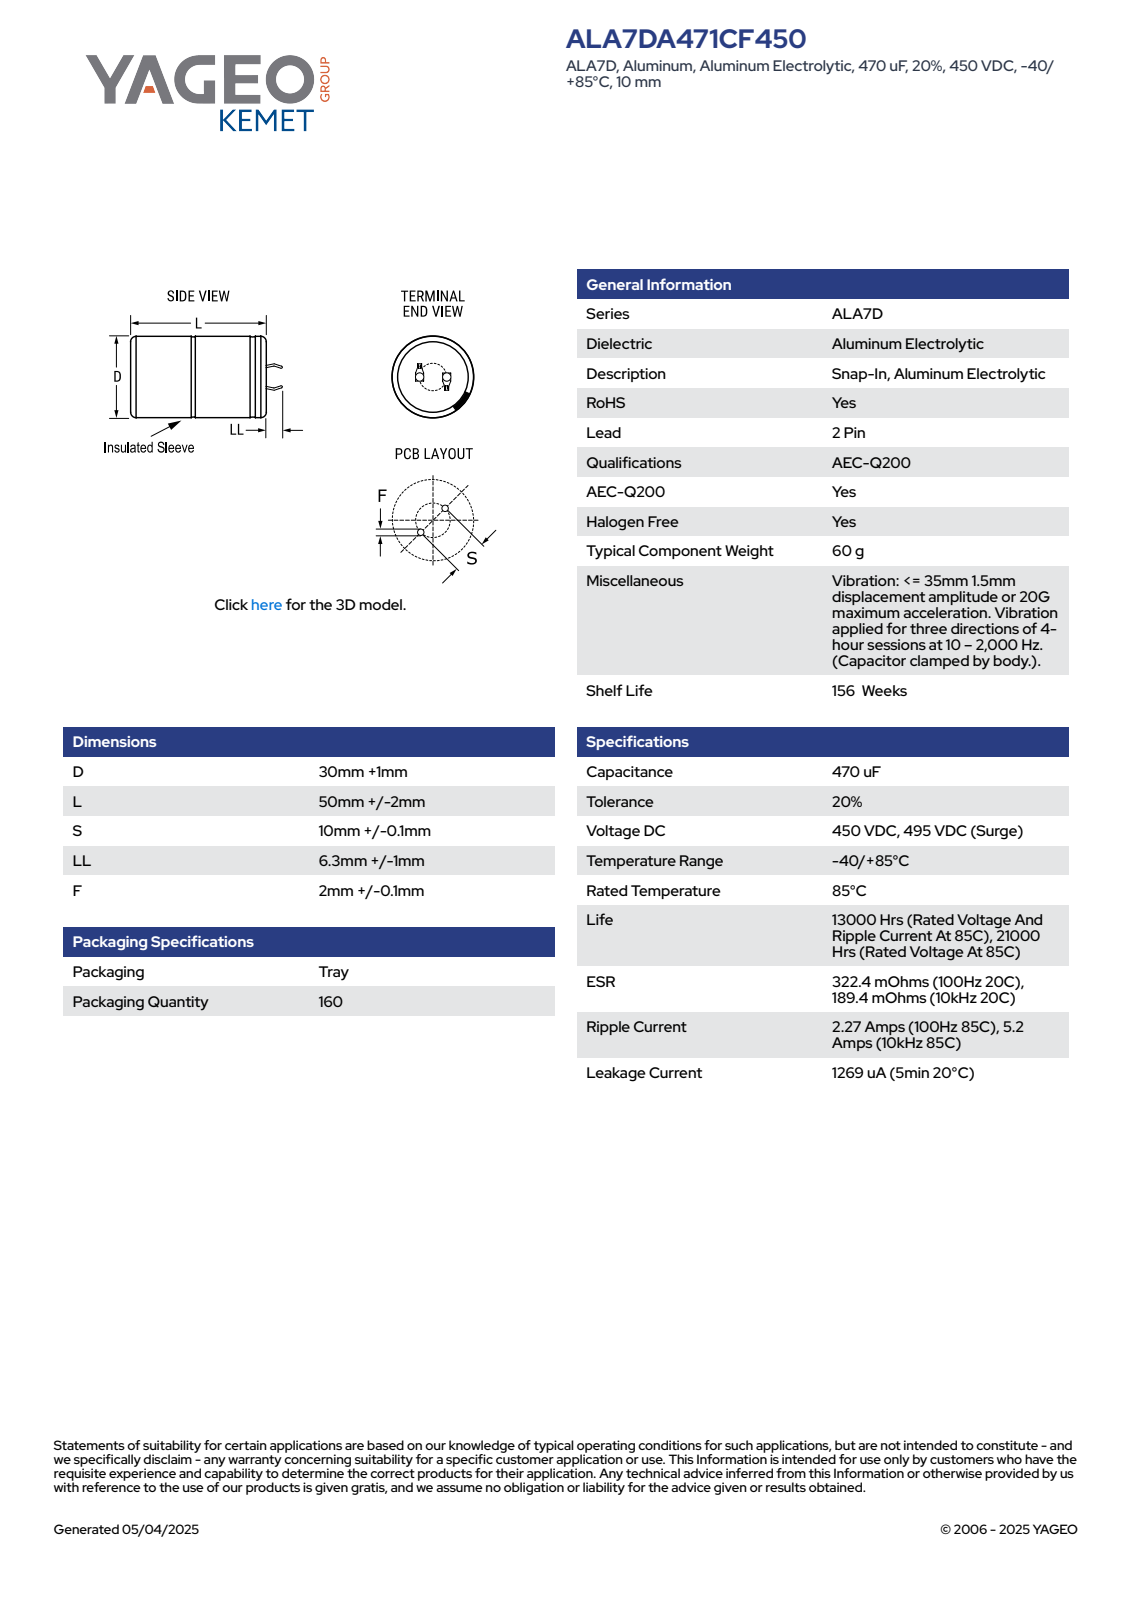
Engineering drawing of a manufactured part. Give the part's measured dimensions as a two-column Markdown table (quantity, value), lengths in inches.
| quantity | value |
| --- | --- |
| part name | CARS_K2PAV_30X50_D31L52S10LL7.3F2.1 |
| STEP written by | SolidWorks 2021 (AUTOMOTIVE_DESIGN) |
| units | inches |
| bodies | 1 solid, 106 faces (52 planar, 11 cylindrical, 43 other) |
| overall size | 2.334 × 1.22 × 1.22 |
| volume | 2.372 in³ |
| surface area | 10.29 in² |
| round holes (diameter × count) | 1.08 × 1 |
| round bosses / shafts (diameter × count) | 1.22 × 1 |
| partial cylindrical surfaces (radius × count) | 0.61 × 1 |
| main face-to-face distances | 2.047, 0.024, 2.067, 0.02, 0.279, 0.301, 0.053, 0.03, 0.302, 0.255 |
